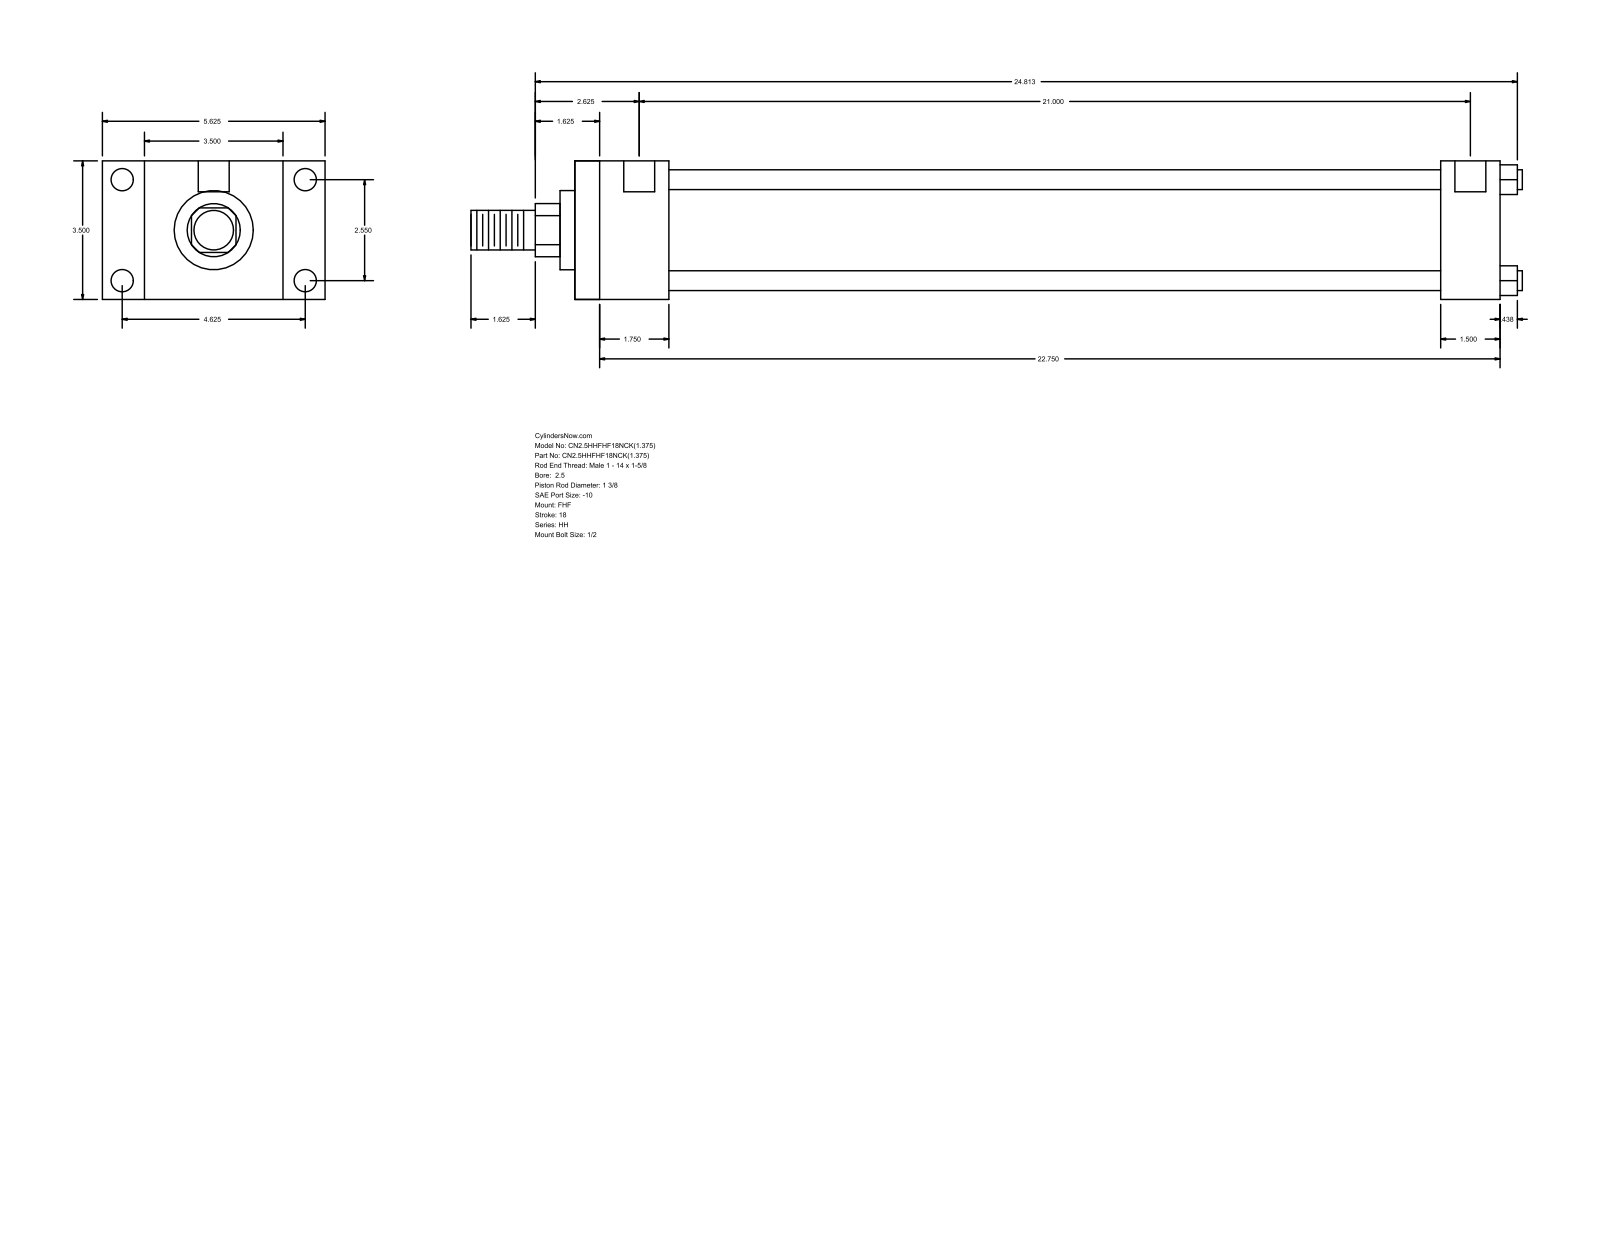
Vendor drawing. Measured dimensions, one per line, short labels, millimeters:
name: HH_FHF__0250_1.375
written by: GSSL Pune (CONFIG_CONTROL_DESIGN)
unit: mm
bodies: 0 solids, 88 faces (60 planar, 28 cylindrical, 0 other)
size: 674.69 × 142.88 × 88.9
holes: 4× ⌀5.56, 4× ⌀14.3, 2× ⌀19.84
bosses: 4× ⌀12.7, 1× ⌀73.03, 1× ⌀50.8, 1× ⌀34.92, 1× ⌀25.4
rounds: 1× R17.06
face distances: 88.9, 60.32, 26.99, 115.89, 593.72, 533.4, 142.88, 555.62, 495.3, 38.1
hole spacings: 1.58, 64.76, 117.48, 134.15, 534.99, 536.57, 533.41
